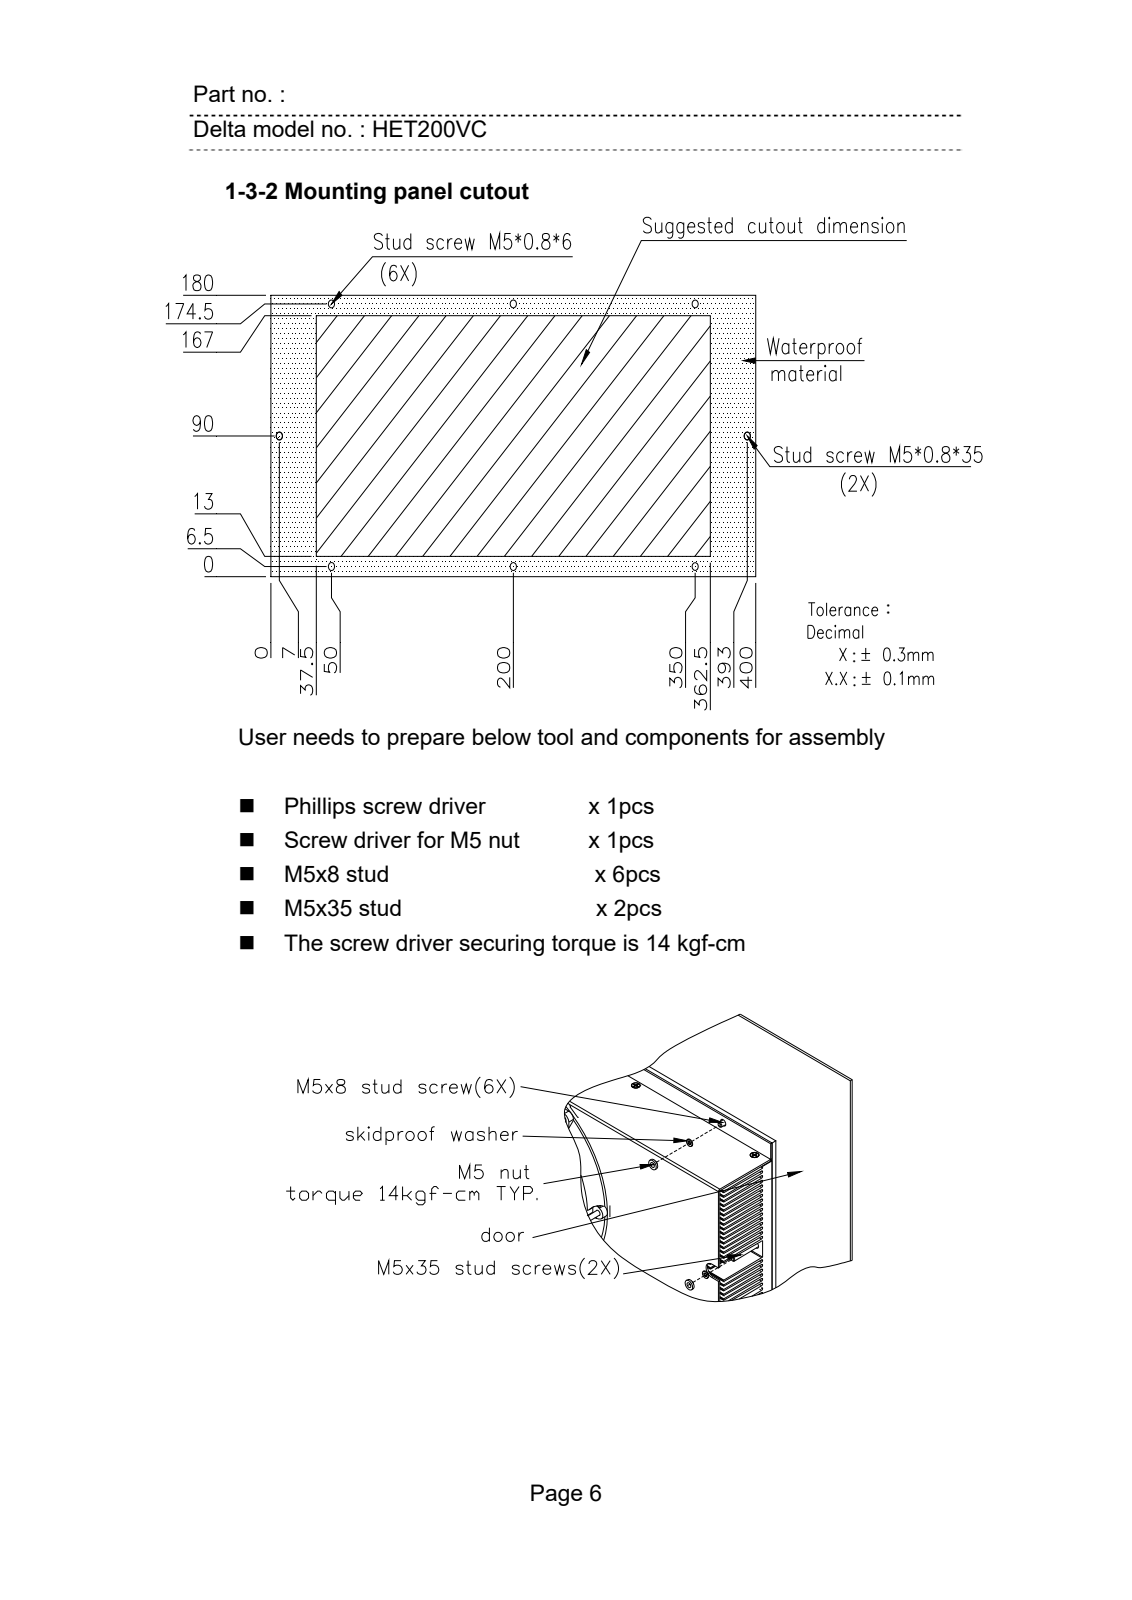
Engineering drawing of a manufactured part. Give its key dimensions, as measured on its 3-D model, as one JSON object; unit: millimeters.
{"part_name": "HET200PC-SOLID", "step_written_by": "CREO PARAMETRIC BY PTC INC, 2015080 (CONFIG_CONTROL_DESIGN)", "units": "millimeters", "bodies": {"solids": 2, "faces": 380, "planar": 183, "cylindrical": 143, "other": 54}, "overall_size": [400, 181, 156.55], "volume_mm3": 1998000, "surface_area_mm2": 546605, "round_holes": [[4, 9], [3, 6], [4.5, 4], [3.5, 3], [2.7, 1], [8, 1]], "partial_cylinders_radius": [[2, 25], [3, 12], [1.5, 7], [0.3, 5], [1.8, 5], [8.5, 4], [10, 4], [4.5, 2]], "face_to_face_distances": [1.5, 77.75, 4, 44.5, 40.5, 38.75, 39, 2, 148.5, 79.25], "hole_center_spacings": [59.74, 105, 143.45, 8, 15.71, 16, 34.44, 62]}
